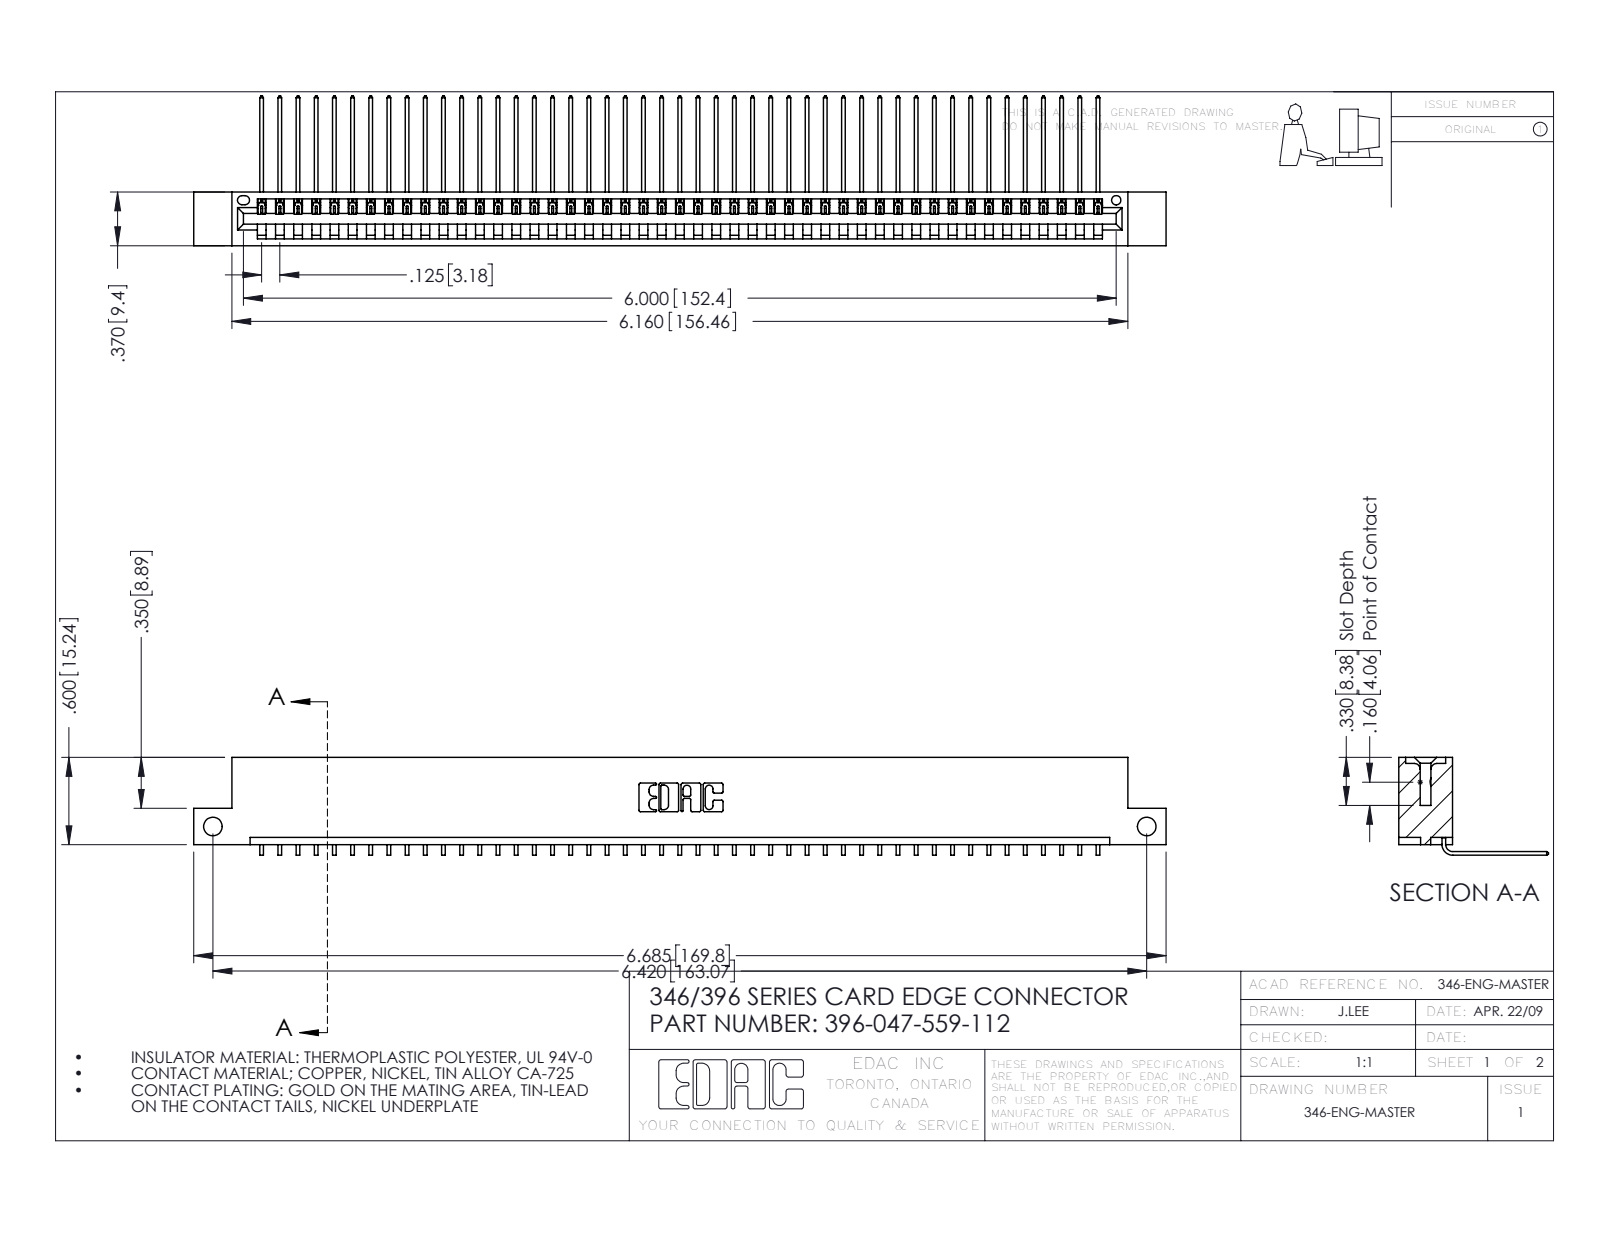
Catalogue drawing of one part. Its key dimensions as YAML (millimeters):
part_name: "396-047-559-112; 345-292-001_558 559 Tail - 1; 346 Part_Flush Mounting Lugs - Side Mount"
step_written_by: "SolidWorks 2016 (CONFIG_CONTROL_DESIGN)"
units: millimeters
bodies: {solids: 48, faces: 2942, planar: 2050, cylindrical: 892, other: 0}
overall_size: [169.8, 26.2, 17.1]
volume: 16400
surface_area: 21280
round_holes:
  - {diameter: 3.3, count: 2}
  - {diameter: 1.6, count: 1}
partial_cylinders:
  - {radius: 0.2, count: 94}
  - {radius: 0.3, count: 22}
  - {radius: 0.2, count: 6}
  - {radius: 0.8, count: 6}
  - {radius: 0.7, count: 3}
  - {radius: 0.8, count: 2}
  - {radius: 1, count: 2}
  - {radius: 0.4, count: 1}
face_to_face_distances: [1.2, 8.2, 9.4, 6.4, 0.6, 1.8, 7.6, 3.8, 5.6, 2.5]
hole_center_spacings: [163.1]
